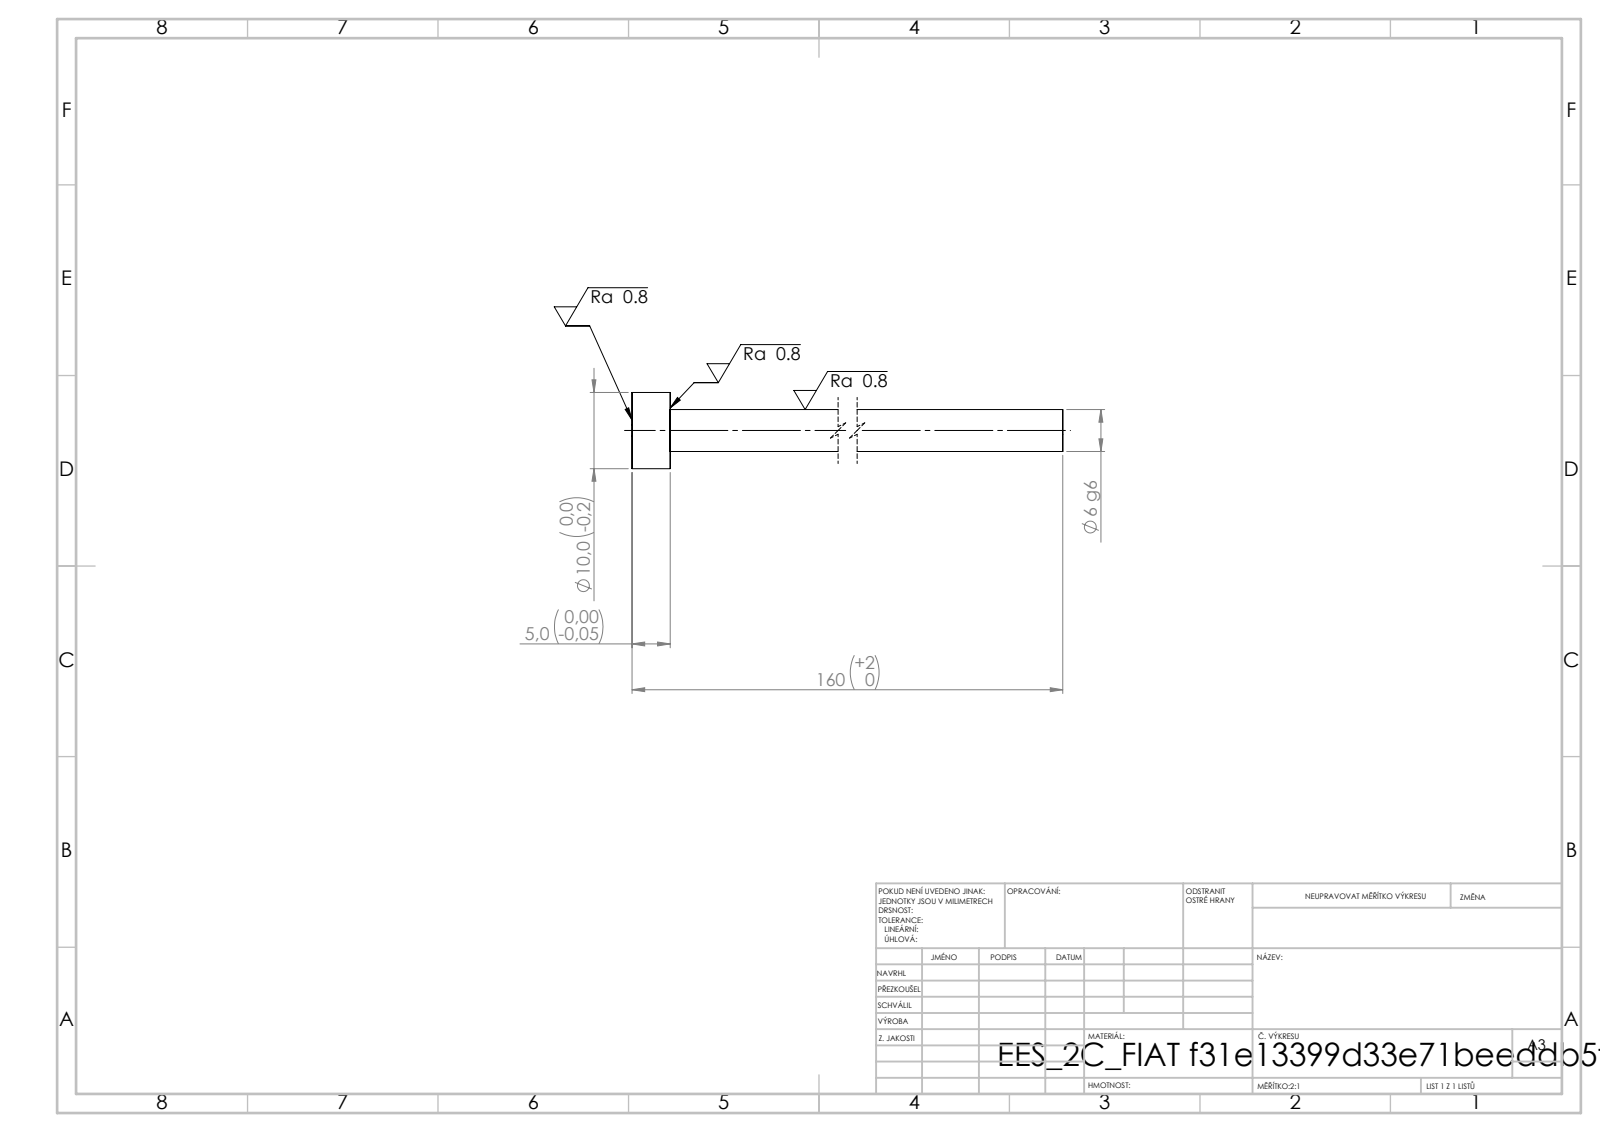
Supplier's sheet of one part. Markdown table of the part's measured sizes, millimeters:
| quantity | value |
| --- | --- |
| STEP written by | SolidWorks 2019 (CONFIG_CONTROL_DESIGN) |
| units | millimeters |
| bodies | 1 solid, 7 faces (3 planar, 4 cylindrical, 0 other) |
| overall size | 160 × 10 × 10 |
| volume | 4 075 mm³ |
| surface area | 2 992 mm² |
| round bosses / shafts (diameter × count) | 10 × 1, 5.5 × 1 |
| main face-to-face distances | 5, 160, 155 |
